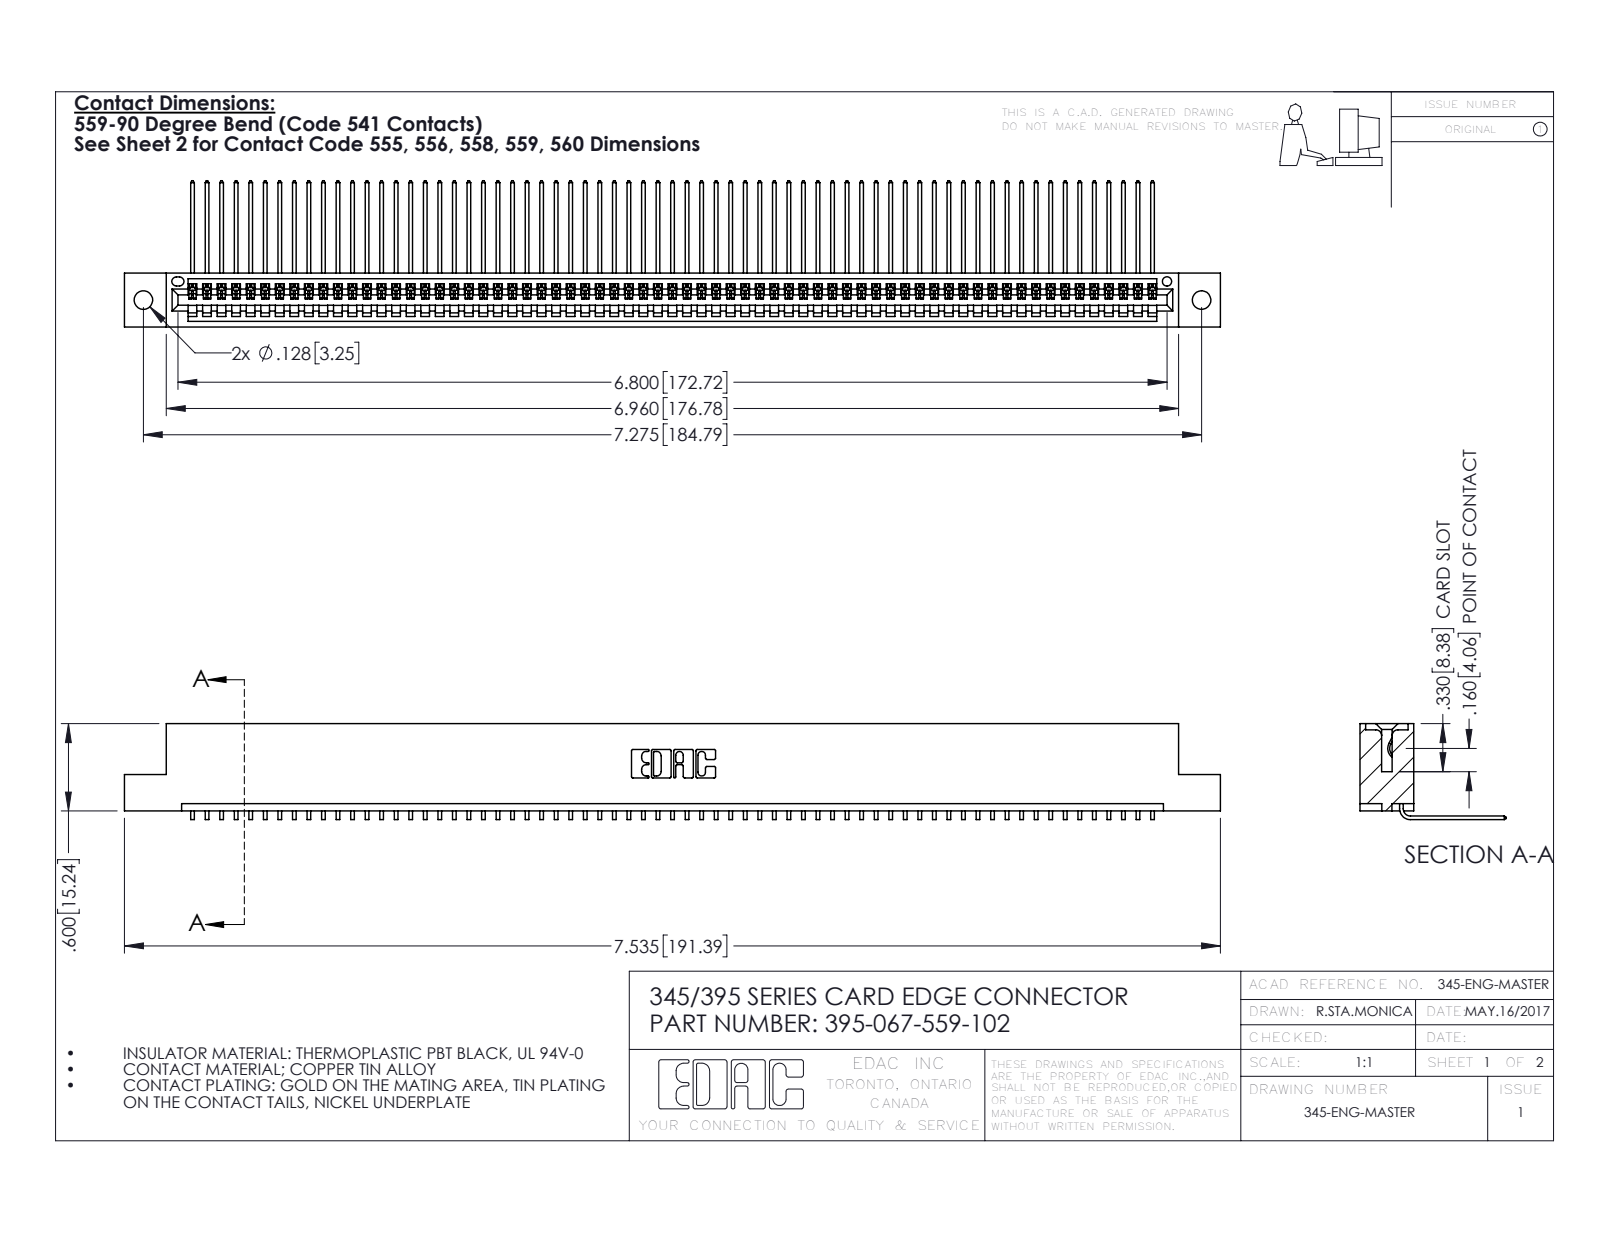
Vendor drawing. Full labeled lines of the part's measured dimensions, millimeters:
Part name (STEP PRODUCT): 345 Part_Flush Mounting Lugs - 0.128 Dia; 395-067-559-102; 345-292-001_558 559 Tail - 1
STEP written by: SolidWorks 2016 (CONFIG_CONTROL_DESIGN)
Units: millimetres
Bodies: 68 solids, 4146 faces (2894 planar, 1252 cylindrical, 0 other)
Overall size (bounding box): 191.4 × 25.5 × 16.7
Volume: 18 570 mm³ · Surface area: 26 060 mm²
Round holes (diameter × count): ⌀3.3 ×2, ⌀1.6 ×1
Partial cylindrical surfaces — rounded edges, fillets, slot ends (radius × count): R0.2 ×134, R0.3 ×22, R0.2 ×6, R0.8 ×6, R0.7 ×3, R0.8 ×2, R1 ×2, R0.4 ×1
Main face-to-face distances: 7.6, 1.8, 9.4, 5.1, 2.5, 6.9, 0.6, 5.7, 3.8, 1.8
Hole centre spacings: 6.9, 178.8, 184.8
